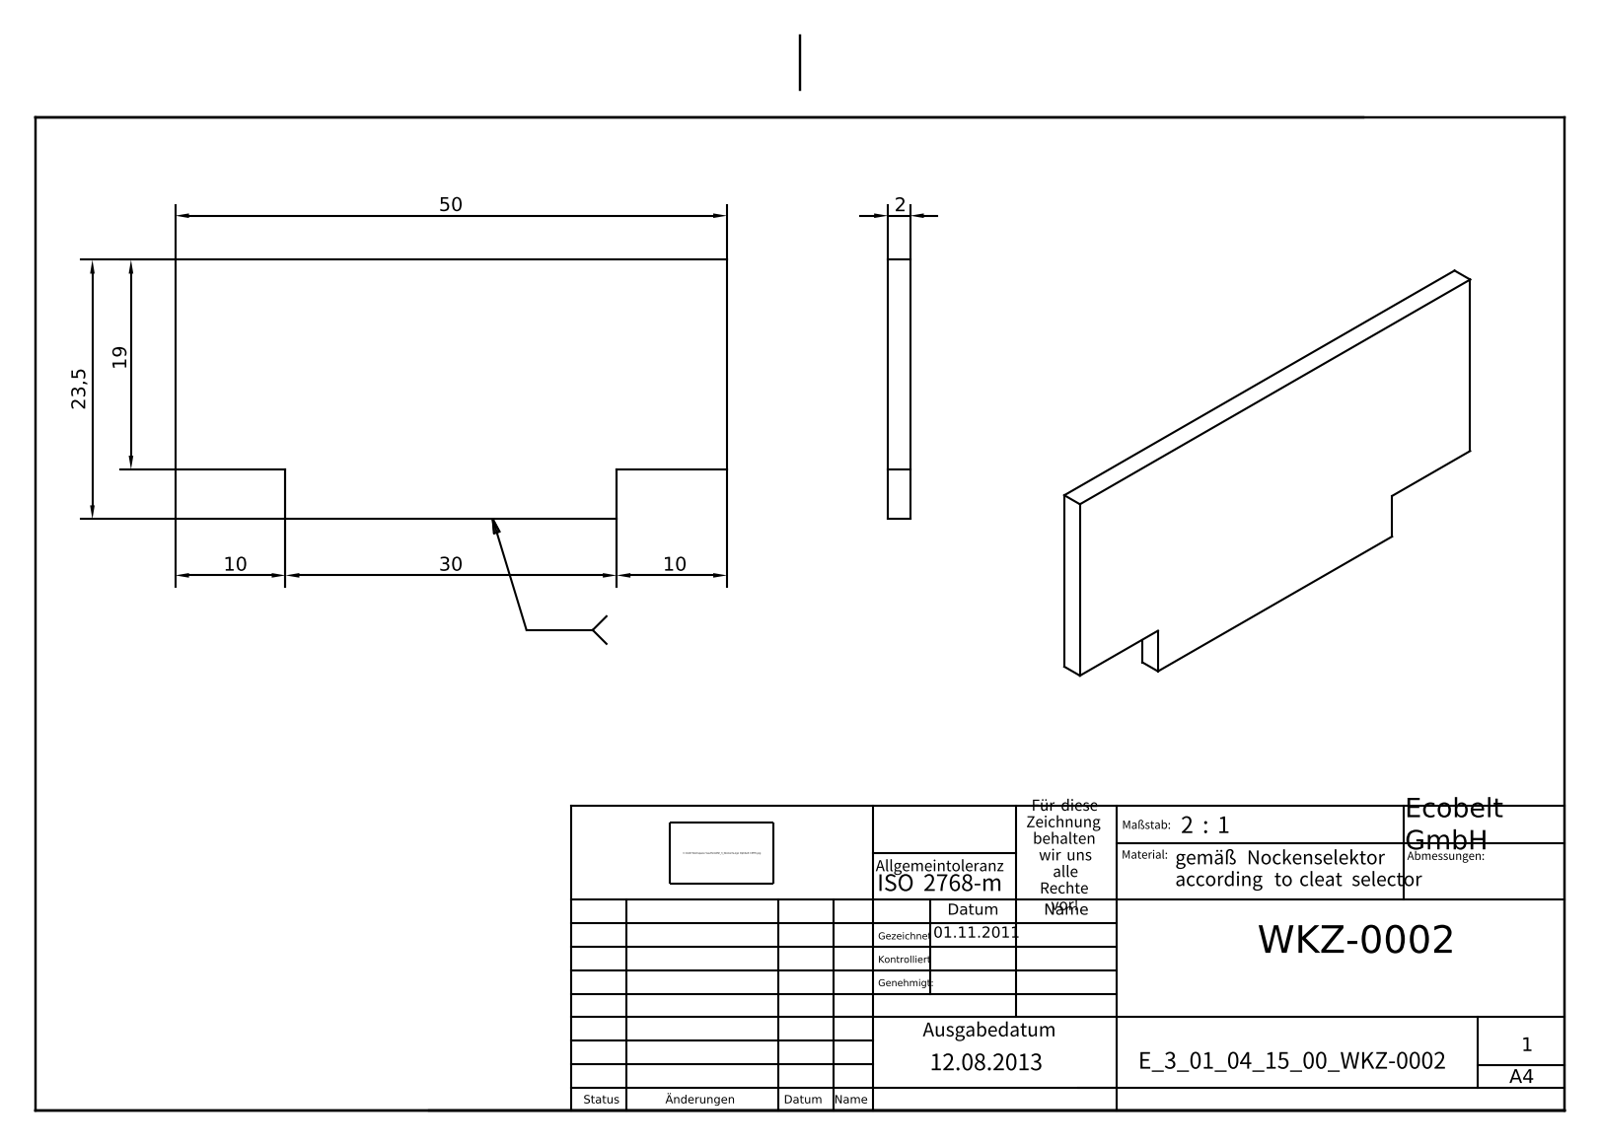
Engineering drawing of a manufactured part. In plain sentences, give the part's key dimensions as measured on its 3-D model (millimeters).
The part is named "E_3_01_04_15_00_WKZ-0002". Its 3-D file was written by "Autodesk Inventor 2021 (AUTOMOTIVE_DESIGN)". It is 1 solid with 10 faces: 10 planar, 0 cylindrical and 0 other. Overall it measures 50 by 23.5 by 2 millimeters. Its volume is 2 170 cubic millimeters and its surface area 2 464 square millimeters. The main face-to-face distances are 2, 23.5, 4.5, 19, 50, 10, 40, 30.
